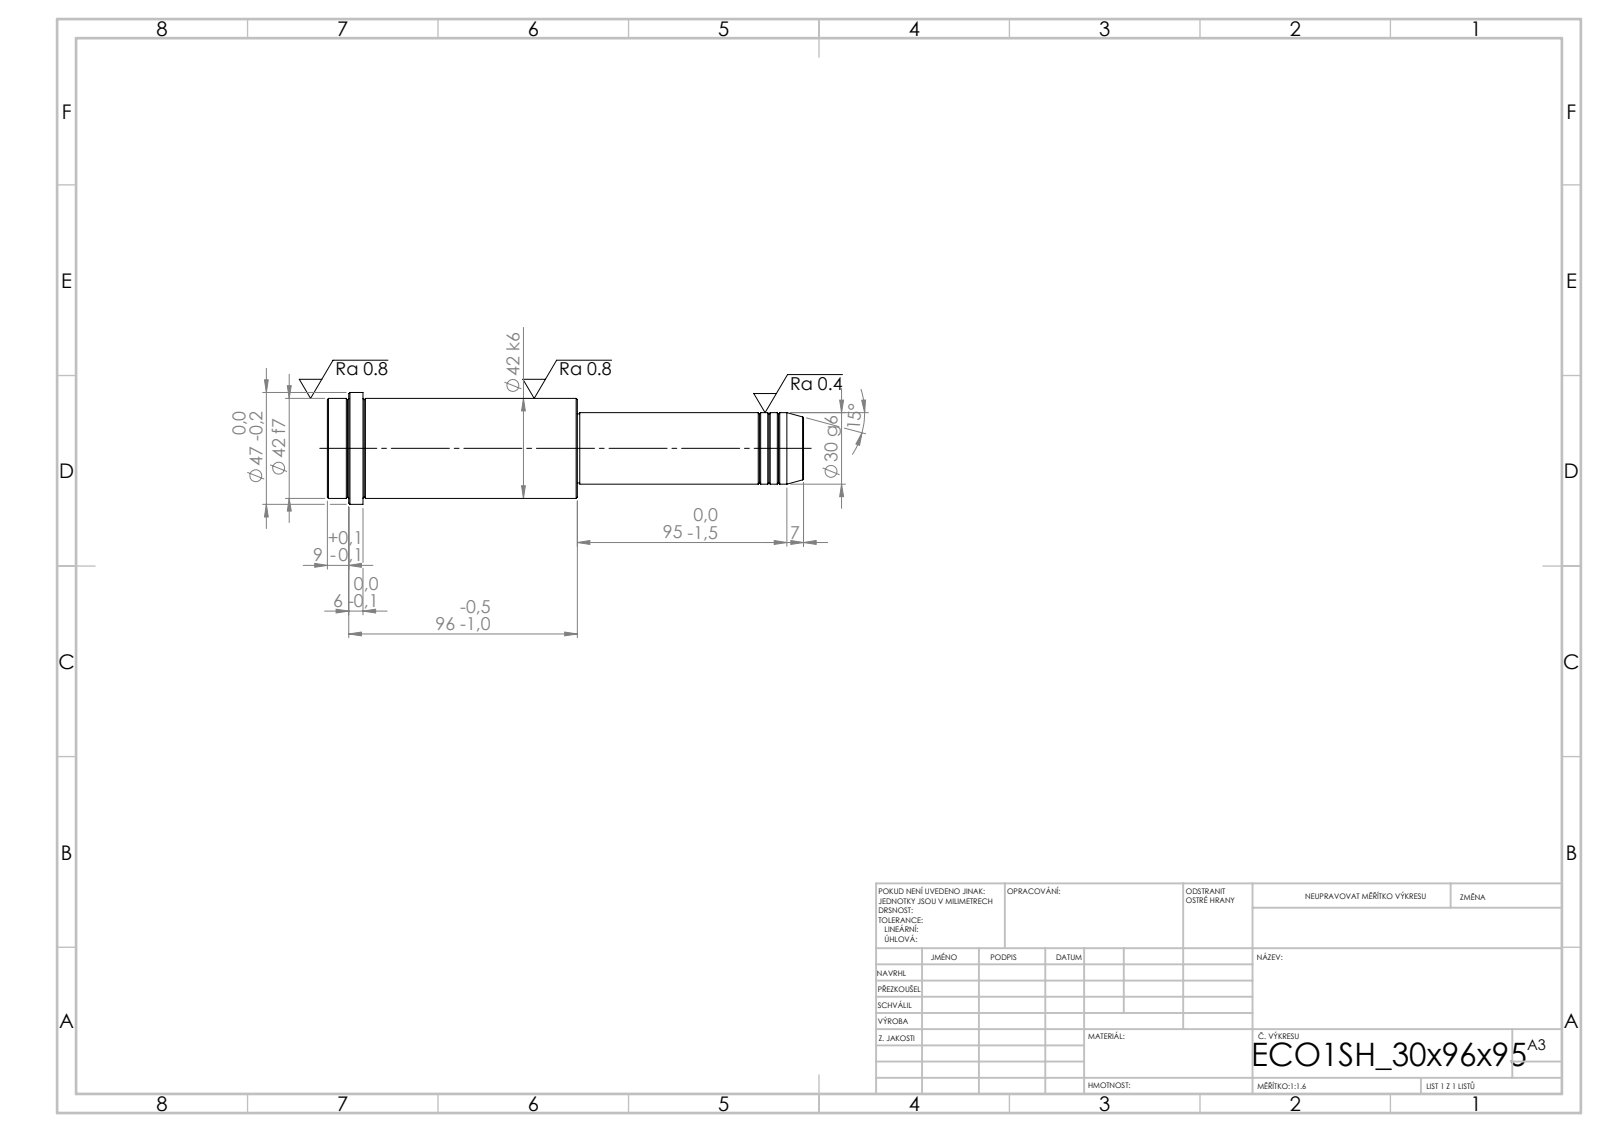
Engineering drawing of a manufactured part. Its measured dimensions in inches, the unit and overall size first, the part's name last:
Units: inches
Overall size (bounding box): 7.874 × 1.85 × 1.85
Round bosses / shafts (diameter × count): ⌀1.85 ×1, ⌀1.654 ×1, ⌀1.181 ×1, ⌀1.142 ×1
Main face-to-face distances: 4.134, 3.74, 7.874, 7.283, 3.543, 0.591, 7.52, 3.78, 0.236, 0.354
Volume: 13.05 in³ · Surface area: 40.99 in²
Bodies: 1 solid, 52 faces (6 planar, 16 cylindrical, 30 other)
STEP written by: SolidWorks 2019 (CONFIG_CONTROL_DESIGN)
